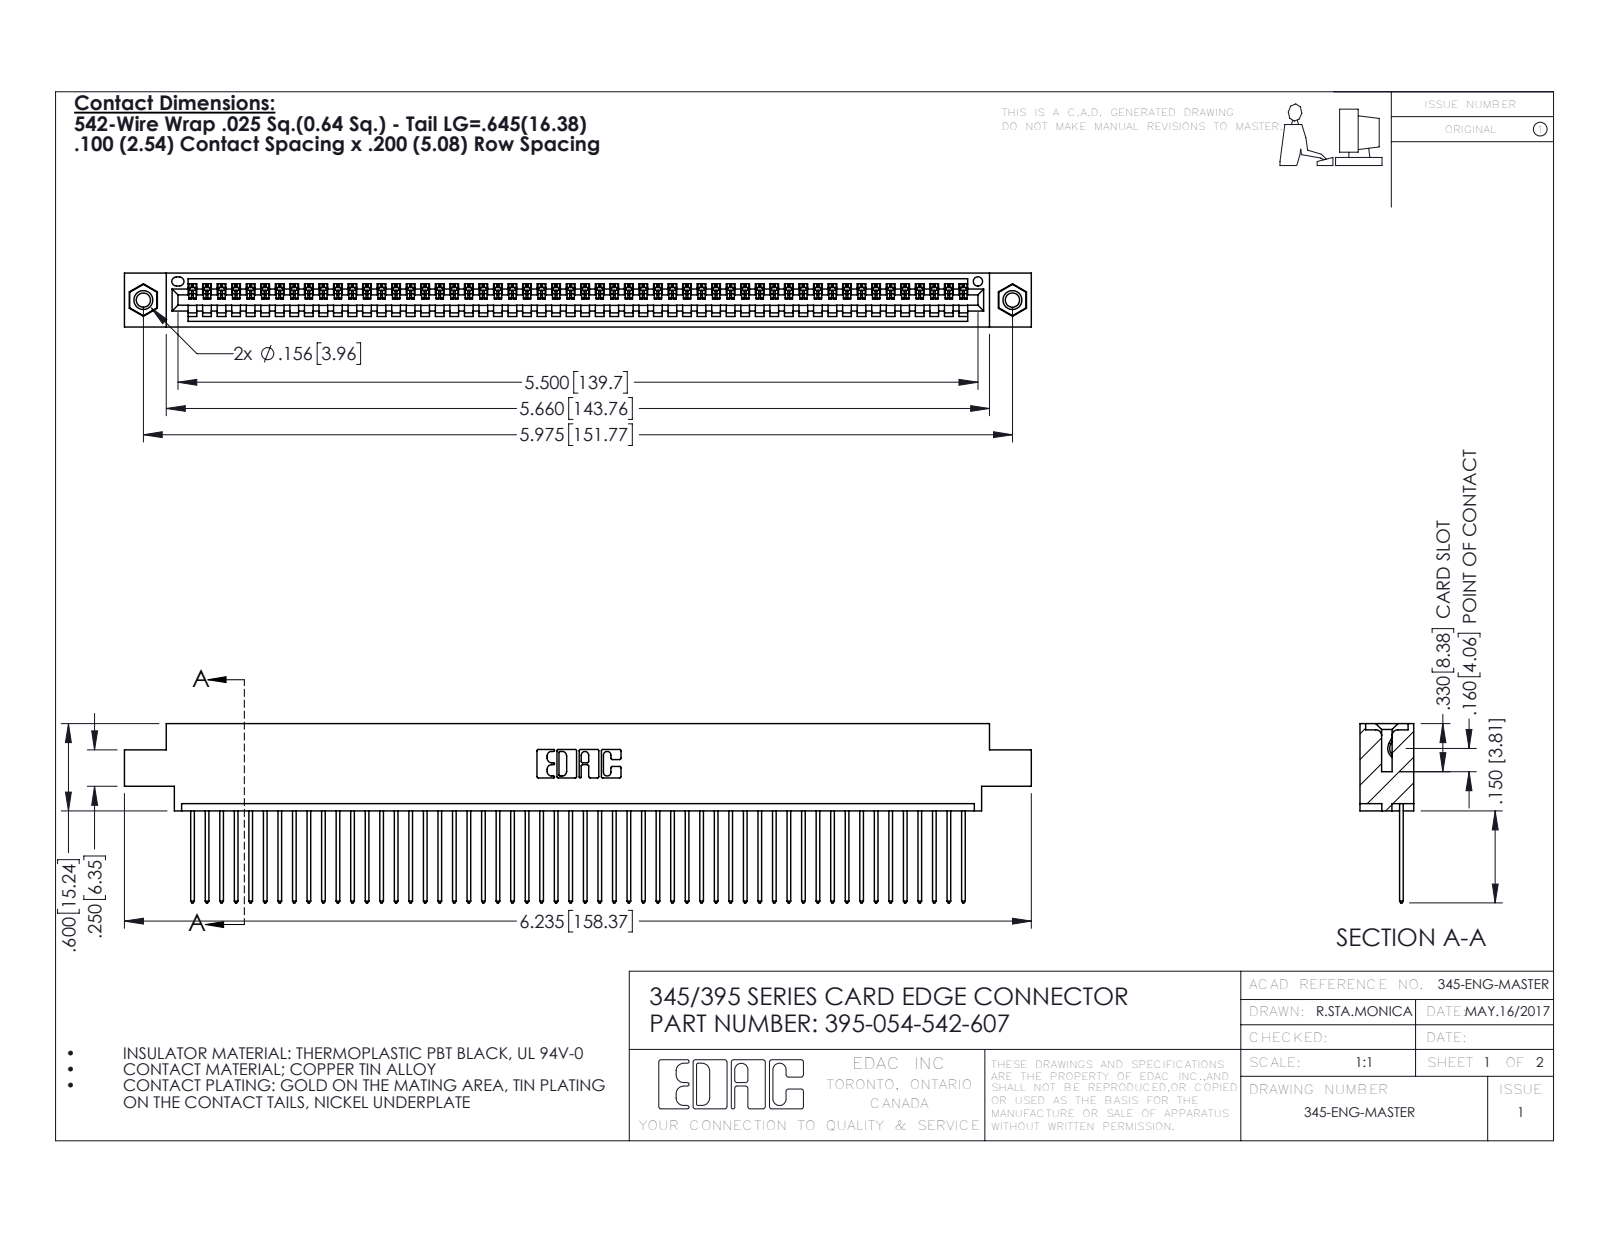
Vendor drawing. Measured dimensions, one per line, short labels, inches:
name: 345 Part_0.170 Offset - 0.156 Dia-TI; 395-054-542-607; 345-250-001_345-250-005-103; 345-292-001_345-293-142
written by: SolidWorks 2016 (CONFIG_CONTROL_DESIGN)
unit: in
bodies: 57 solids, 3322 faces (2276 planar, 1030 cylindrical, 16 other)
size: 6.235 × 1.232 × 0.37
volume: 0.924 in³; area: 32.85 in²
holes: 2× ⌀0.098, 2× ⌀0.125, 2× ⌀0.156, 1× ⌀0.064
bosses: 2× ⌀0.155
rounds: 108× R0.006, 108× R0.01, 22× R0.01, 6× R0.007, 6× R0.031, 3× R0.026, 2× R0.031, 2× R0.04
face distances: 0.072, 0.298, 0.37, 0.098, 0.272, 0.025, 0.2, 0.225, 0.175, 0.149
hole spacings: 0.27, 5.739, 5.975
